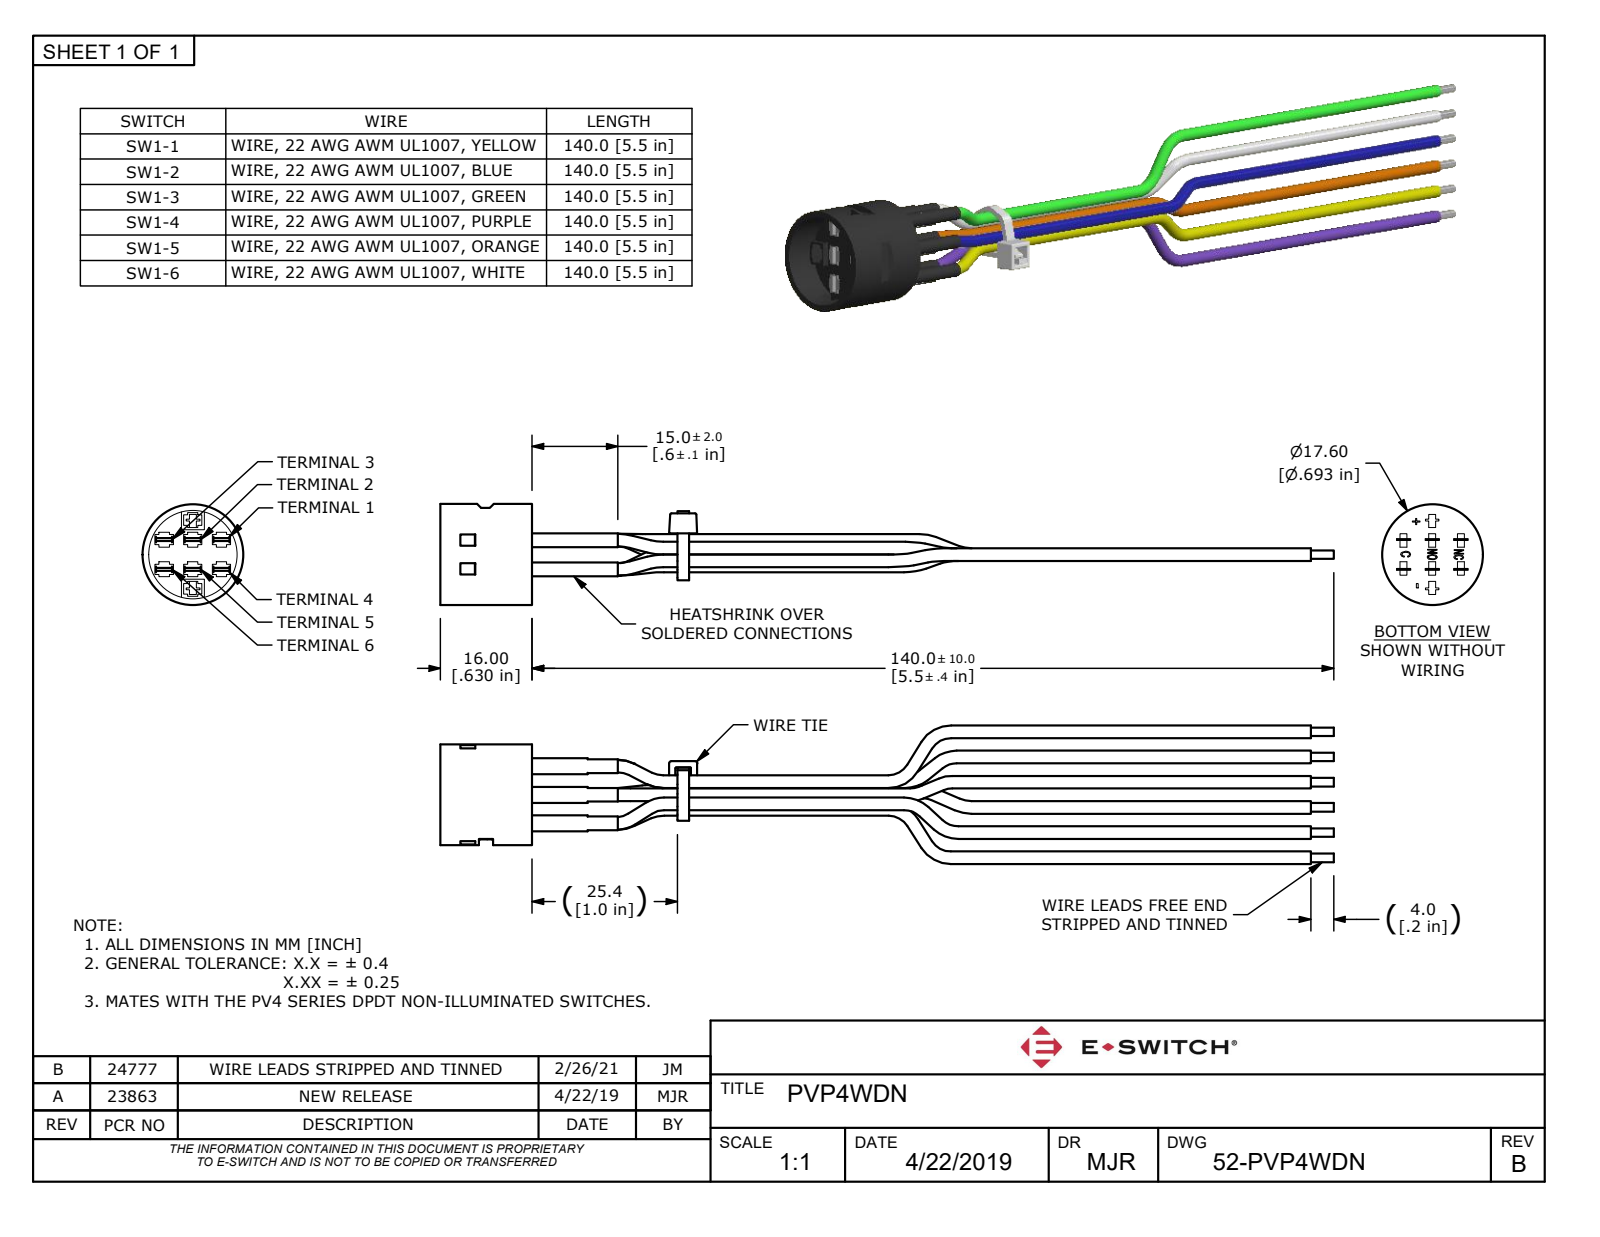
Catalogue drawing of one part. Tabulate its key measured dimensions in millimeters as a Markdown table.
| quantity | value |
| --- | --- |
| part name | PVP4WDN |
| STEP written by | Autodesk Inventor 2018 (AP242_MANAGED_MODEL_BASED_3D_ENGINEERING_MIM_LF) |
| units | millimeters |
| bodies | 1 solid, 823 faces (612 planar, 112 cylindrical, 99 other) |
| overall size | 156 × 24.2 × 17.6 |
| volume | 5 736 mm³ |
| surface area | 9 340 mm² |
| round holes (diameter × count) | 2.2 × 6, 15.4 × 1 |
| round bosses / shafts (diameter × count) | 2.2 × 24, 2.4 × 6, 1.5 × 6, 17.6 × 1 |
| partial cylindrical surfaces (radius × count) | 0.2 × 14, 0.25 × 12, 2 × 5, 0.75 × 4, 1.1 × 4, 0.7 × 2 |
| main face-to-face distances | 5.2, 0.5, 5.7, 9.9, 0.4, 4.7, 2, 5, 2.2, 6.1 |
| hole center spacings | 5, 7.14, 5.1, 5.59, 5.64, 10, 11.23, 2.5 |
